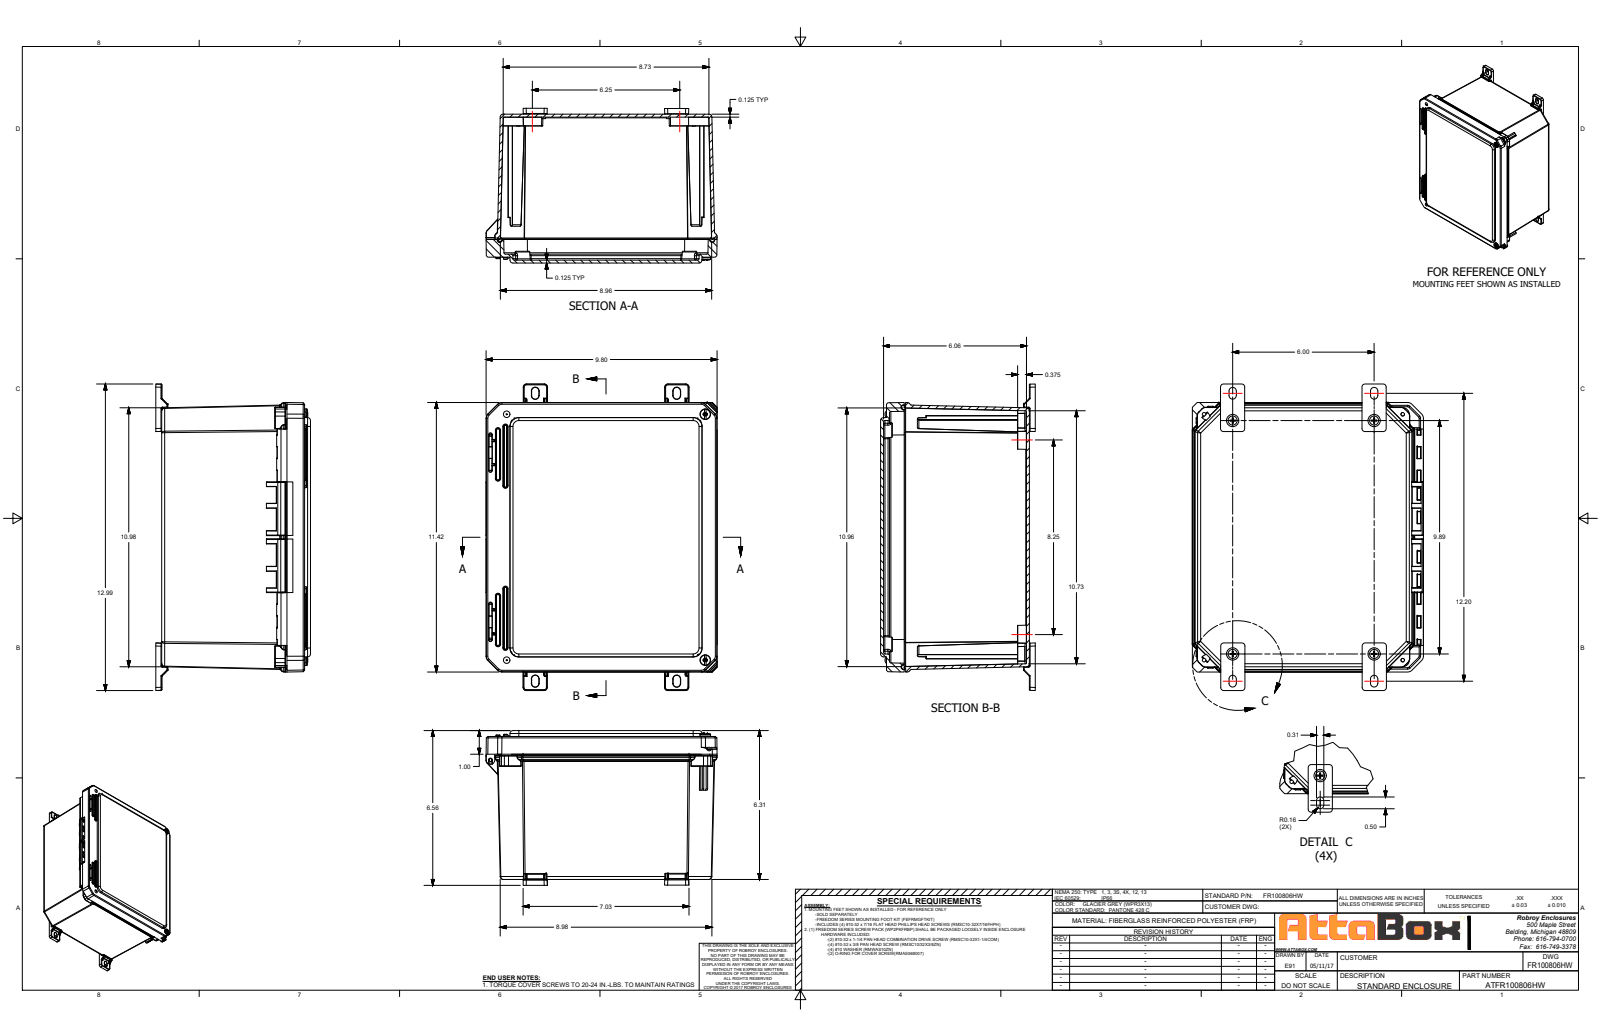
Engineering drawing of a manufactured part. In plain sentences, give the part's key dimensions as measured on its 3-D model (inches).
The part is named "FR100806HW". Its 3-D file was written by "SolidWorks 2021 (AUTOMOTIVE_DESIGN)". It is 7 solids with 2031 faces: 605 planar, 800 cylindrical and 626 other. Overall it measures 11.424 by 9.8 by 6.31 inches. Its volume is 70.14 cubic inches and its surface area 974 square inches. Round holes: 8 of diameter 0.152, 4 of diameter 0.252, 4 of diameter 0.253, 2 of diameter 0.219, 2 of diameter 0.227, 2 of diameter 0.313, 1 of diameter 0.137. Round bosses or shafts: 4 of diameter 0.87, 2 of diameter 0.45, 2 of diameter 0.435, 2 of diameter 0.199, 1 of diameter 0.135. Partial cylindrical surfaces (rounded edges, fillets, slot ends): 160 of radius 0.01, 80 of radius 0.005, 57 of radius 0.02, 45 of radius 0.03, 24 of radius 0.03, 24 of radius 0.09, 24 of radius 0.096, 22 of radius 0.125. The main face-to-face distances are 0.125, 6.06, 0.125, 6.31, 6.185, 0.127, 0.126, 6.185, 0.25, 5.935. The hole center spacings are 9.776, 10.229, 12.457, 0.946, 1.24, 7.216, 9.399, 10.422.
